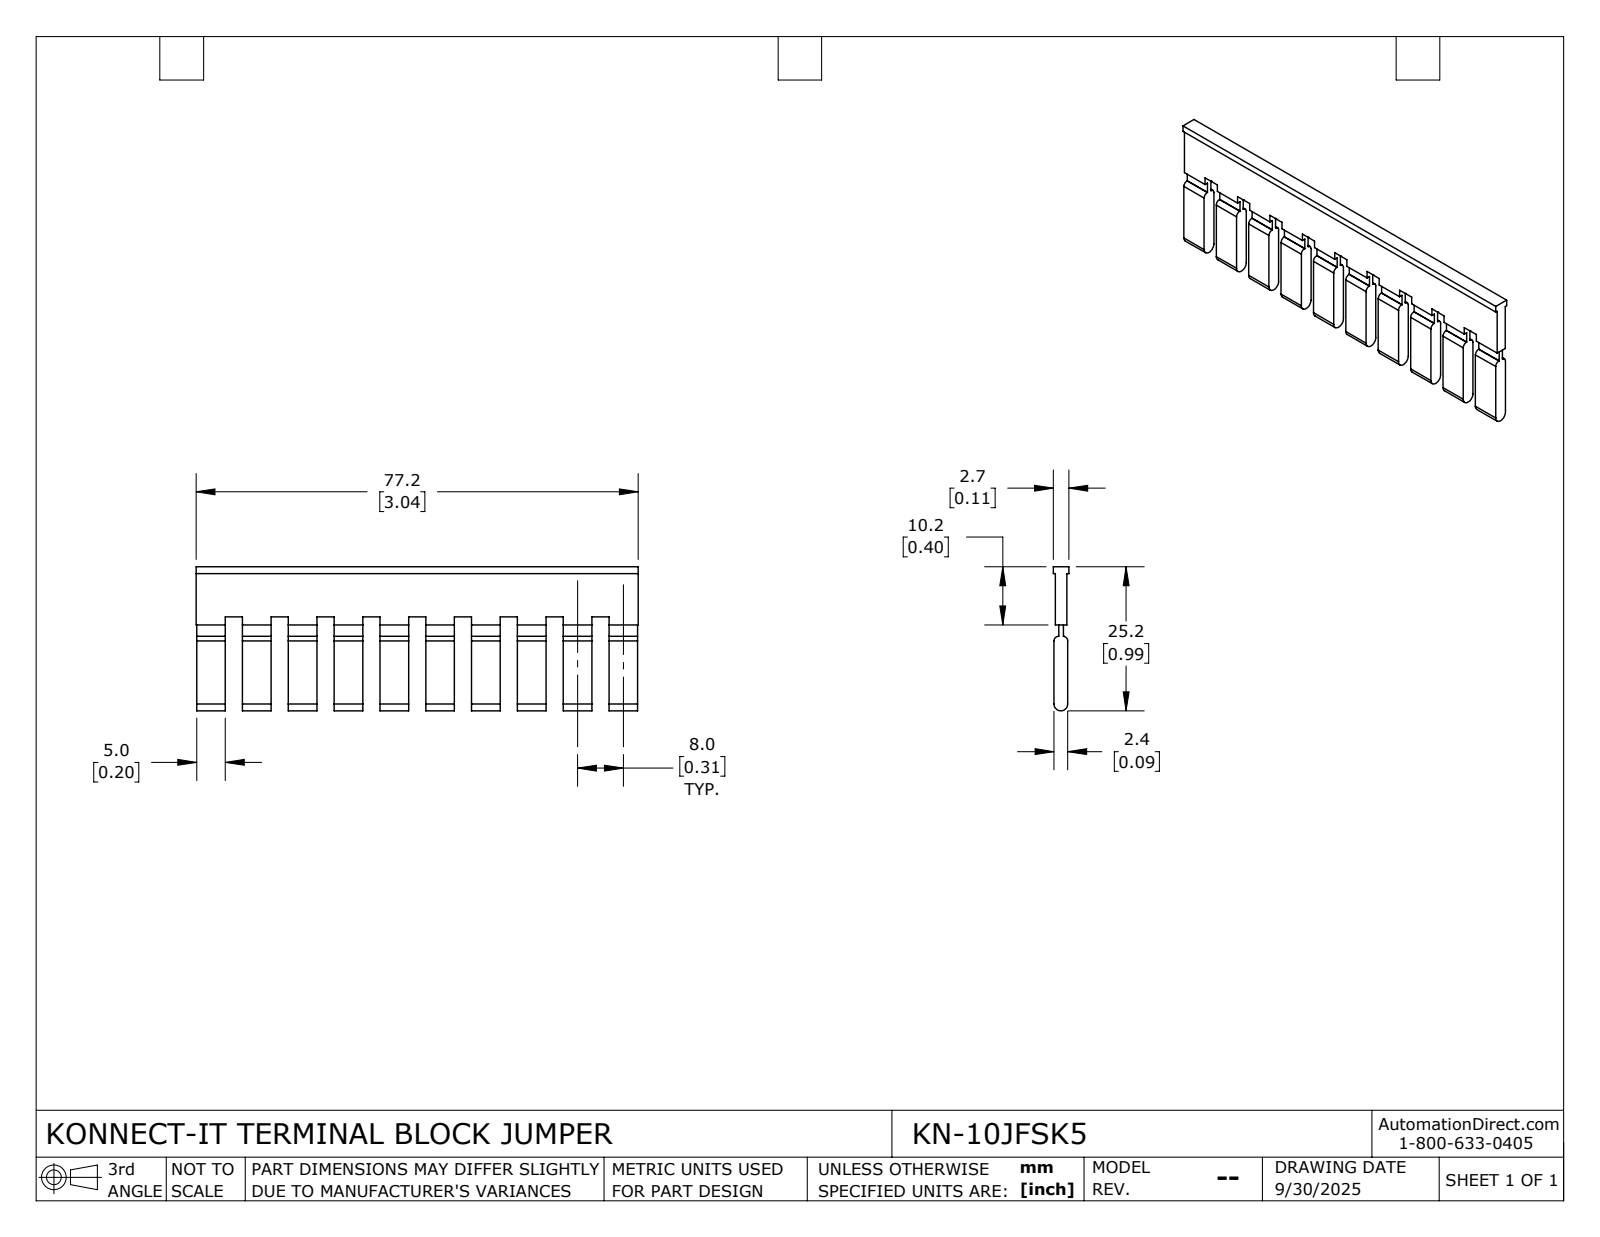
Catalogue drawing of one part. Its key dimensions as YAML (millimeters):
part_name: "KN-10JFSK5"
step_written_by: "SolidWorks 2024 (CONFIG_CONTROL_DESIGN)"
units: millimeters
bodies: {solids: 1, faces: 146, planar: 106, cylindrical: 40, other: 0}
overall_size: [77.2, 25.15, 2.7]
volume: 3152
surface_area: 4214
partial_cylinders:
  - {radius: 0.8, count: 3}
  - {radius: 1.2, count: 1}
face_to_face_distances: [2, 8, 2.15, 2.4, 2.25, 16, 24, 32, 40, 5]
